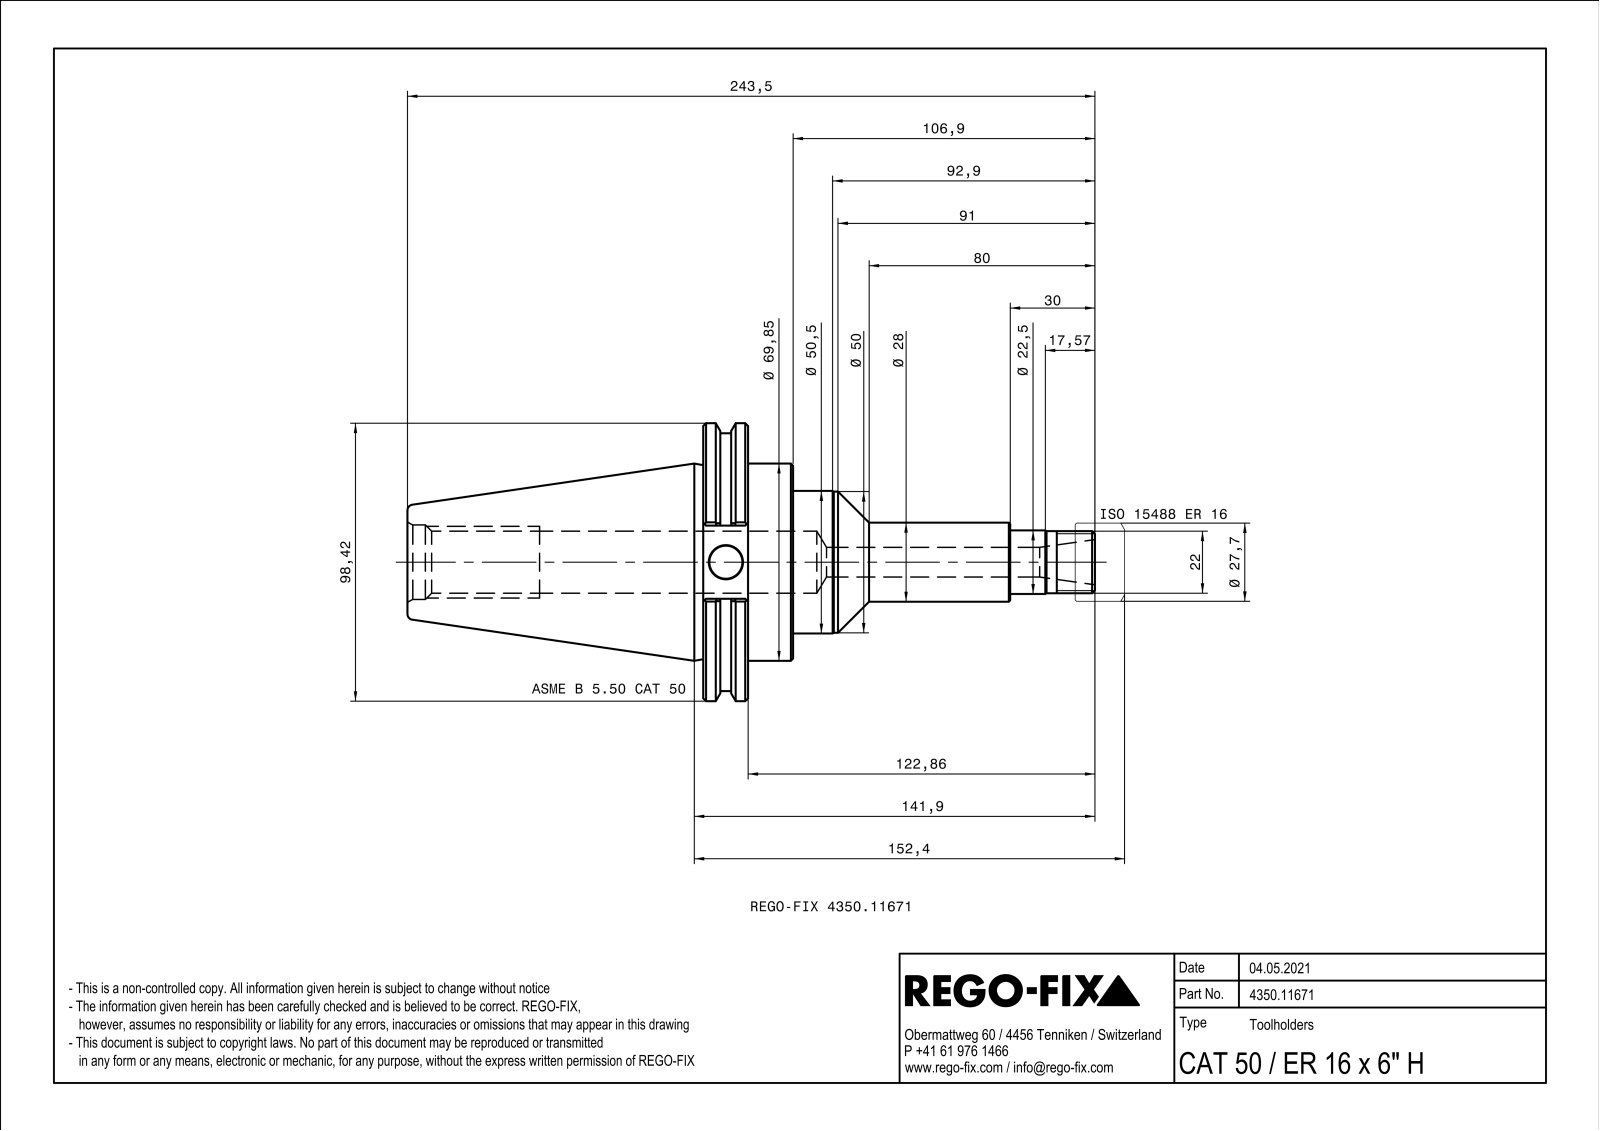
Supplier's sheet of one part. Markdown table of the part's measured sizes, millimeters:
| quantity | value |
| --- | --- |
| part name | NOCUT |
| STEP written by | SIEMENS PLM Software Solid Edge ST10 (AUTOMOTIVE_DESIGN) |
| units | millimeters |
| bodies | 1 solid, 125 faces (32 planar, 35 cylindrical, 58 other) |
| overall size | 243.5 × 98.42 × 94.39 |
| volume | 446 099 mm³ |
| surface area | 62 281 mm² |
| round holes (diameter × count) | 10.5 × 1, 11.7 × 1, 21.96 × 1, 21.96 × 1, 26.4 × 1 |
| round bosses / shafts (diameter × count) | 98.42 × 1, 91.3 × 1, 69.85 × 1, 50.5 × 1, 50 × 1, 28 × 1, 22.5 × 1, 22 × 1 |
| partial cylindrical surfaces (radius × count) | 0.5 × 12 |
| main face-to-face distances | 15.87, 15.96, 31.83, 136.6, 120.64, 104.77, 72.73, 25.92, 106.9, 122.86 |
